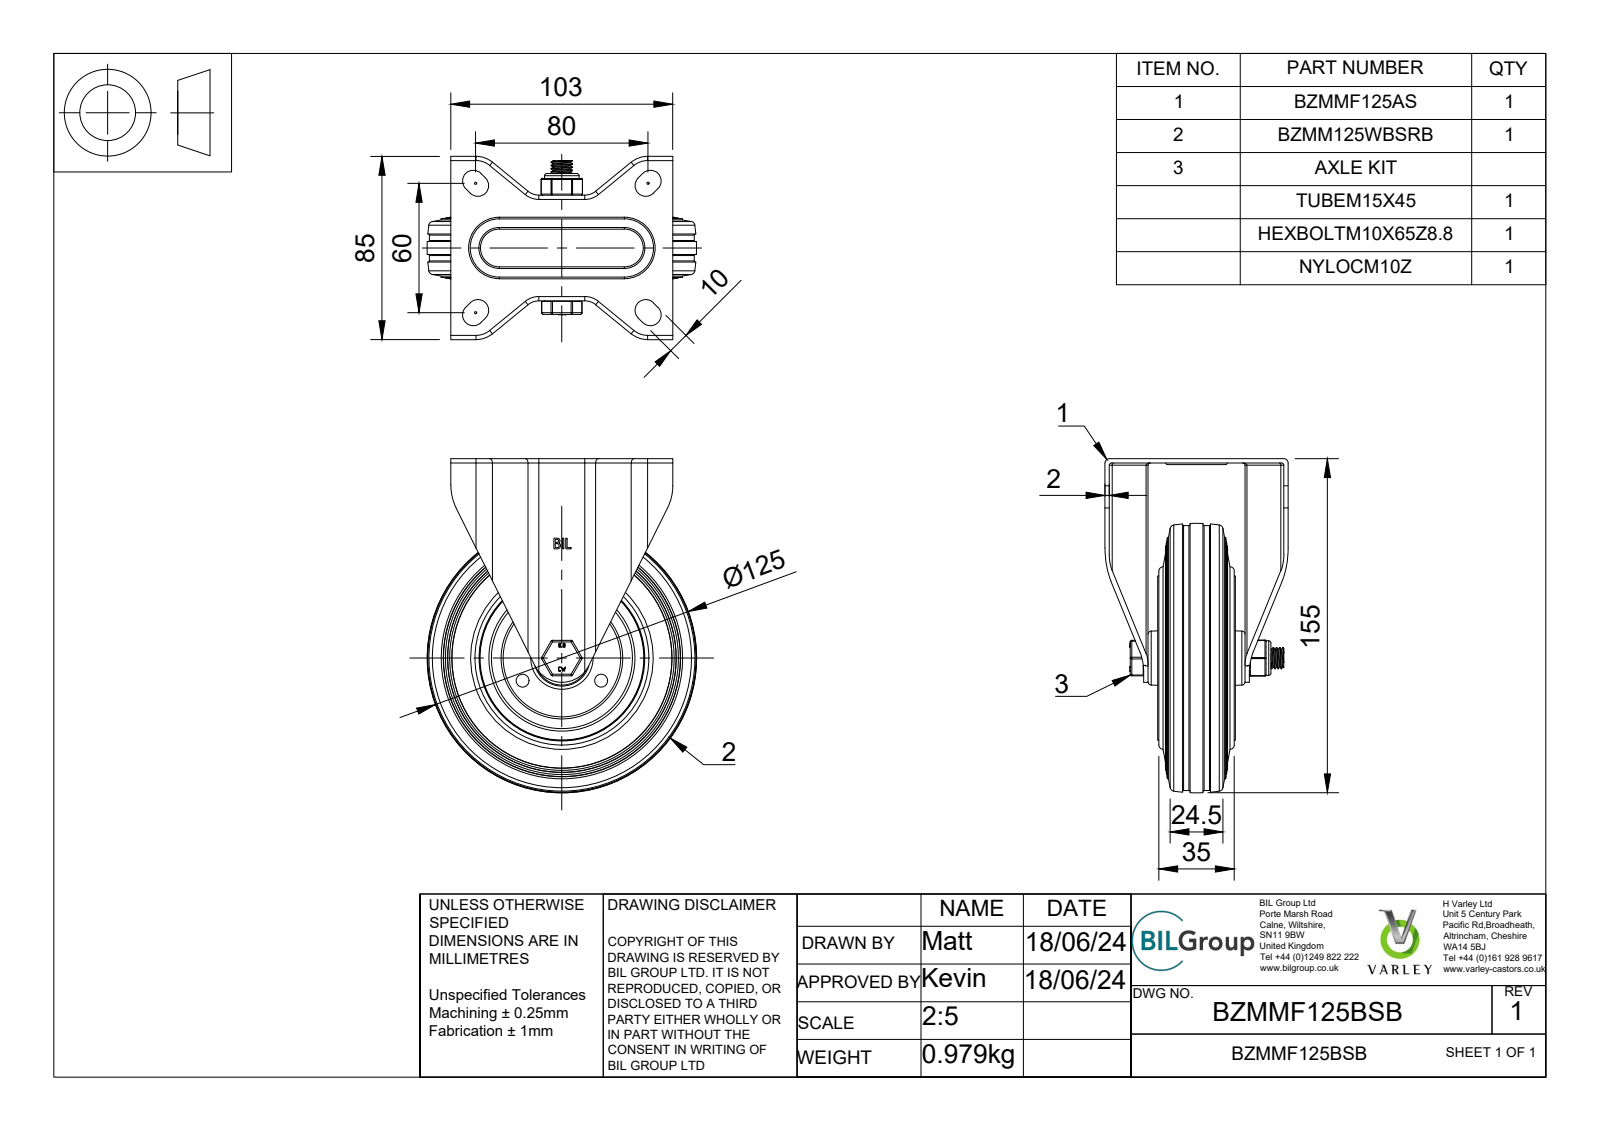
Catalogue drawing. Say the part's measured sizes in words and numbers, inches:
The part is named "BZMMF125BSB v3; BZMMF125AS v1; BZMMF125AS; ZINC PLATED, PRESSED STEEL BRACKET (+7 more)". Its 3-D file was written by "Autodesk Translation Framework v13.14.0.145 (AUTOMOTIVE_DESIGN)". It is 19 solids with 617 faces: 219 planar, 232 cylindrical and 166 other. Overall it measures 6.102 by 4.921 by 3.346 inches. Its volume is 20.92 cubic inches and its surface area 199.6 square inches. Round holes: 3 of diameter 0.157, 1 of diameter 0.394, 1 of diameter 0.402, 1 of diameter 0.472, 1 of diameter 0.591, 1 of diameter 0.908, 1 of diameter 2.297, 1 of diameter 3.007. Round bosses or shafts: 8 of diameter 0.157, 3 of diameter 0.236, 1 of diameter 4.838, 1 of diameter 0.896, 1 of diameter 0.63, 1 of diameter 0.589, 1 of diameter 0.388, 1 of diameter 0.32. Partial cylindrical surfaces (rounded edges, fillets, slot ends): 20 of radius 0.03, 18 of radius 0.02, 8 of radius 0.039, 8 of radius 0.079, 8 of radius 0.197, 4 of radius 0.157, 4 of radius 0.236, 4 of radius 0.315. The main face-to-face distances are 0.079, 0.742, 0.906, 1.85, 0.827, 0.945, 0.663, 1.024, 0.82, 0.709. The hole center spacings are 0.828, 1.434, 0.828, 1.435.
